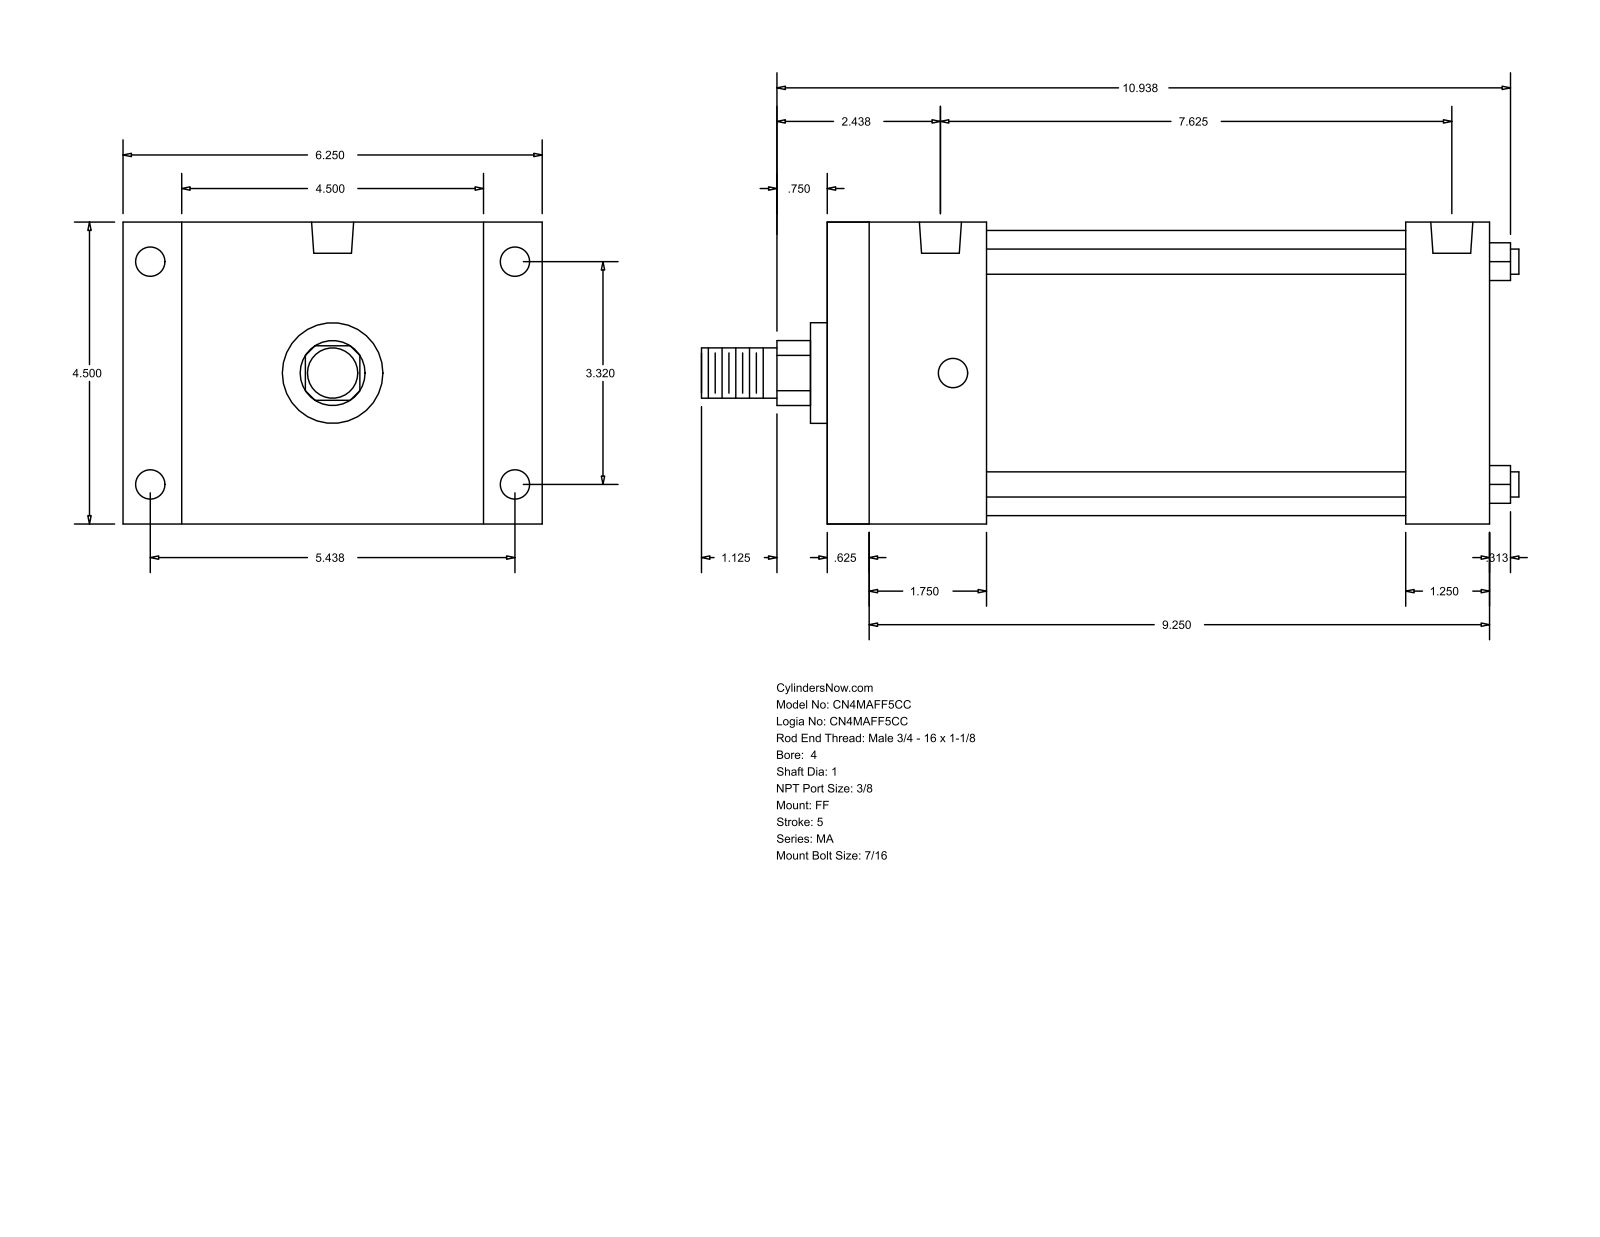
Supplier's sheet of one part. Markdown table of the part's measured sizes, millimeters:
| quantity | value |
| --- | --- |
| part name | MA_FF__0400_1 |
| STEP written by | GSSL Pune (CONFIG_CONTROL_DESIGN) |
| units | millimeters |
| bodies | 0 solids, 92 faces (64 planar, 28 cylindrical, 0 other) |
| overall size | 309.56 × 158.75 × 114.3 |
| round holes (diameter × count) | 11.11 × 8, 15.93 × 2 |
| round bosses / shafts (diameter × count) | 9.53 × 4, 107.95 × 1, 38.1 × 1, 25.4 × 1, 19.05 × 1 |
| partial cylindrical surfaces (radius × count) | 12.29 × 1 |
| main face-to-face distances | 114.3, 250.83, 15.87, 234.96, 22.23, 136.53, 219.07, 203.2, 31.76, 60.33 |
| hole center spacings | 84.32, 138.12, 161.82, 184.15, 4.76, 4.77, 188.91, 188.92 |
